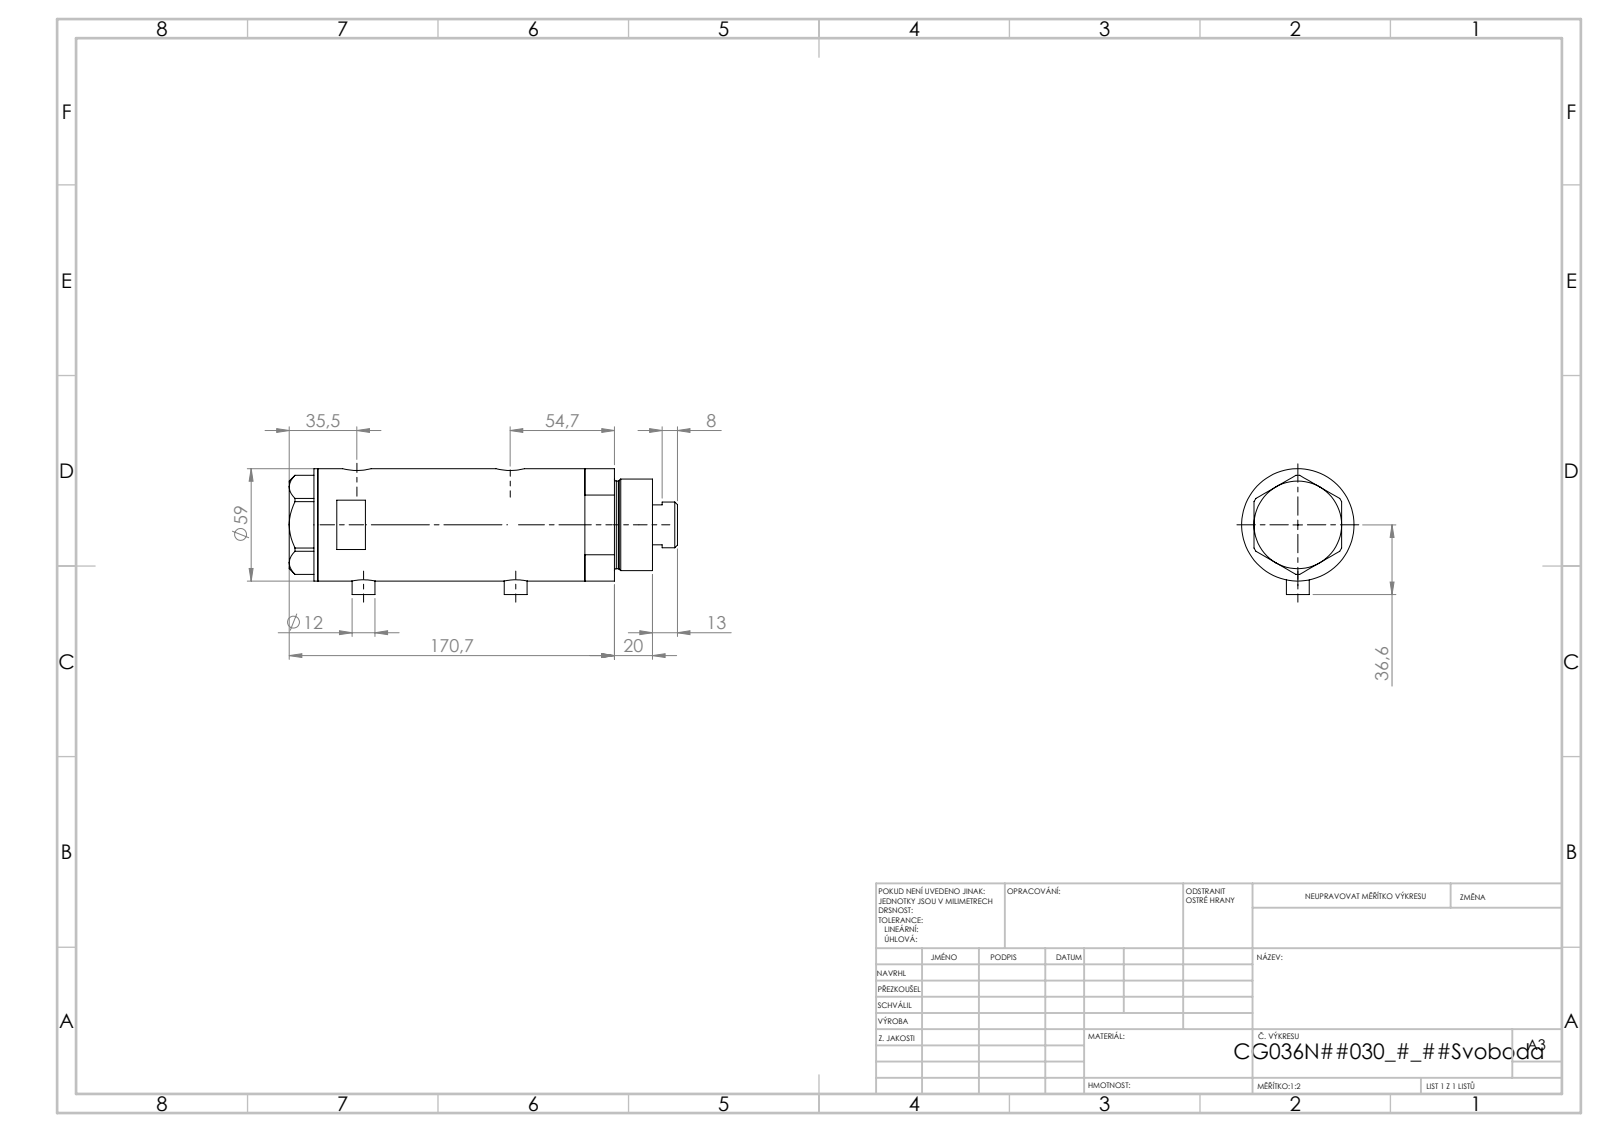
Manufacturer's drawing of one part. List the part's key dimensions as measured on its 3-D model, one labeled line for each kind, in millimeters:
Part name (STEP PRODUCT): V270CG_VC; V270CG_BACK; V270CG_FRONT; V270CG_MIDDLE
STEP written by: SolidWorks 2019 (CONFIG_CONTROL_DESIGN)
Units: millimetres
Bodies: 4 solids, 126 faces (53 planar, 53 cylindrical, 20 other)
Overall size (bounding box): 203.8 × 66.1 × 59
Volume: 472 487 mm³ · Surface area: 98 949 mm²
Round holes (diameter × count): ⌀5 ×2, ⌀9.73 ×2, ⌀12.5 ×2, ⌀15 ×2, ⌀8.5 ×1, ⌀25 ×1, ⌀26.5 ×1, ⌀36 ×1, ⌀40 ×1, ⌀52 ×1
Round bosses / shafts (diameter × count): ⌀12 ×2, ⌀59 ×1, ⌀48 ×1, ⌀46 ×1, ⌀24 ×1
Main face-to-face distances: 102.2, 23.5, 78.7, 15, 38.5, 117.2, 2, 175.7, 190.7, 152.2
Hole centre spacings: 2.9, 3.5, 77, 79.9, 80.5, 83.4
